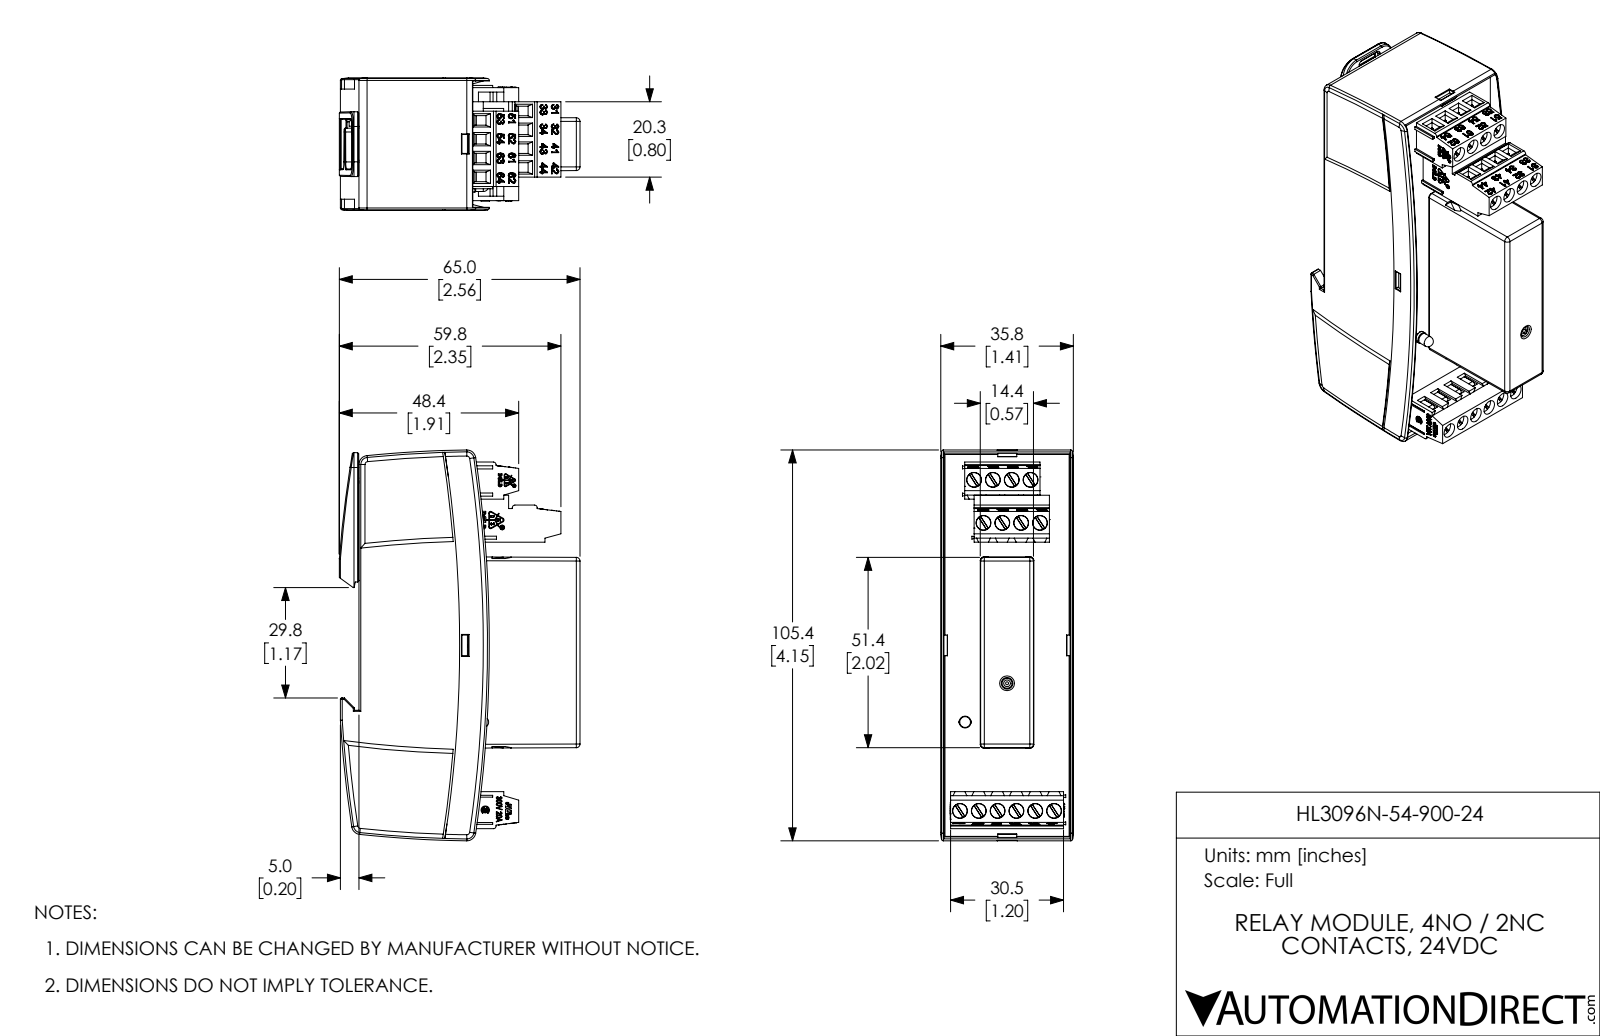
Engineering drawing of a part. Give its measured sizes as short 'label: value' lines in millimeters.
name: HL3096N-54-900-24
written by: SolidWorks 2017 (AUTOMOTIVE_DESIGN)
unit: mm
bodies: 1 solid, 3802 faces (2495 planar, 609 cylindrical, 698 other)
size: 105.4 × 64.9 × 35.8
volume: 147 100 mm³; area: 32 750 mm²
holes: 27× ⌀1.5, 14× ⌀4, 2× ⌀0.6, 2× ⌀0.9, 1× ⌀0.5, 1× ⌀0.9, 1× ⌀0.9, 1× ⌀1.3, 1× ⌀1.5
bosses: 14× ⌀3.9, 2× ⌀0.5, 1× ⌀3.2, 1× ⌀2.9, 1× ⌀1.2, 1× ⌀0.9, 1× ⌀0.9, 1× ⌀0.8
rounds: 48× R0.2, 23× R0.5, 21× R0.2, 15× R0.3, 10× R1, 7× R0.1, 6× R0.1, 6× R0.1
face distances: 35.6, 29.3, 0.7, 35.8, 35.4, 35, 0.8, 34.7, 30.4, 34.1
hole spacings: 10, 5.1, 5, 11.2, 10.2, 14.1, 11.9, 15
